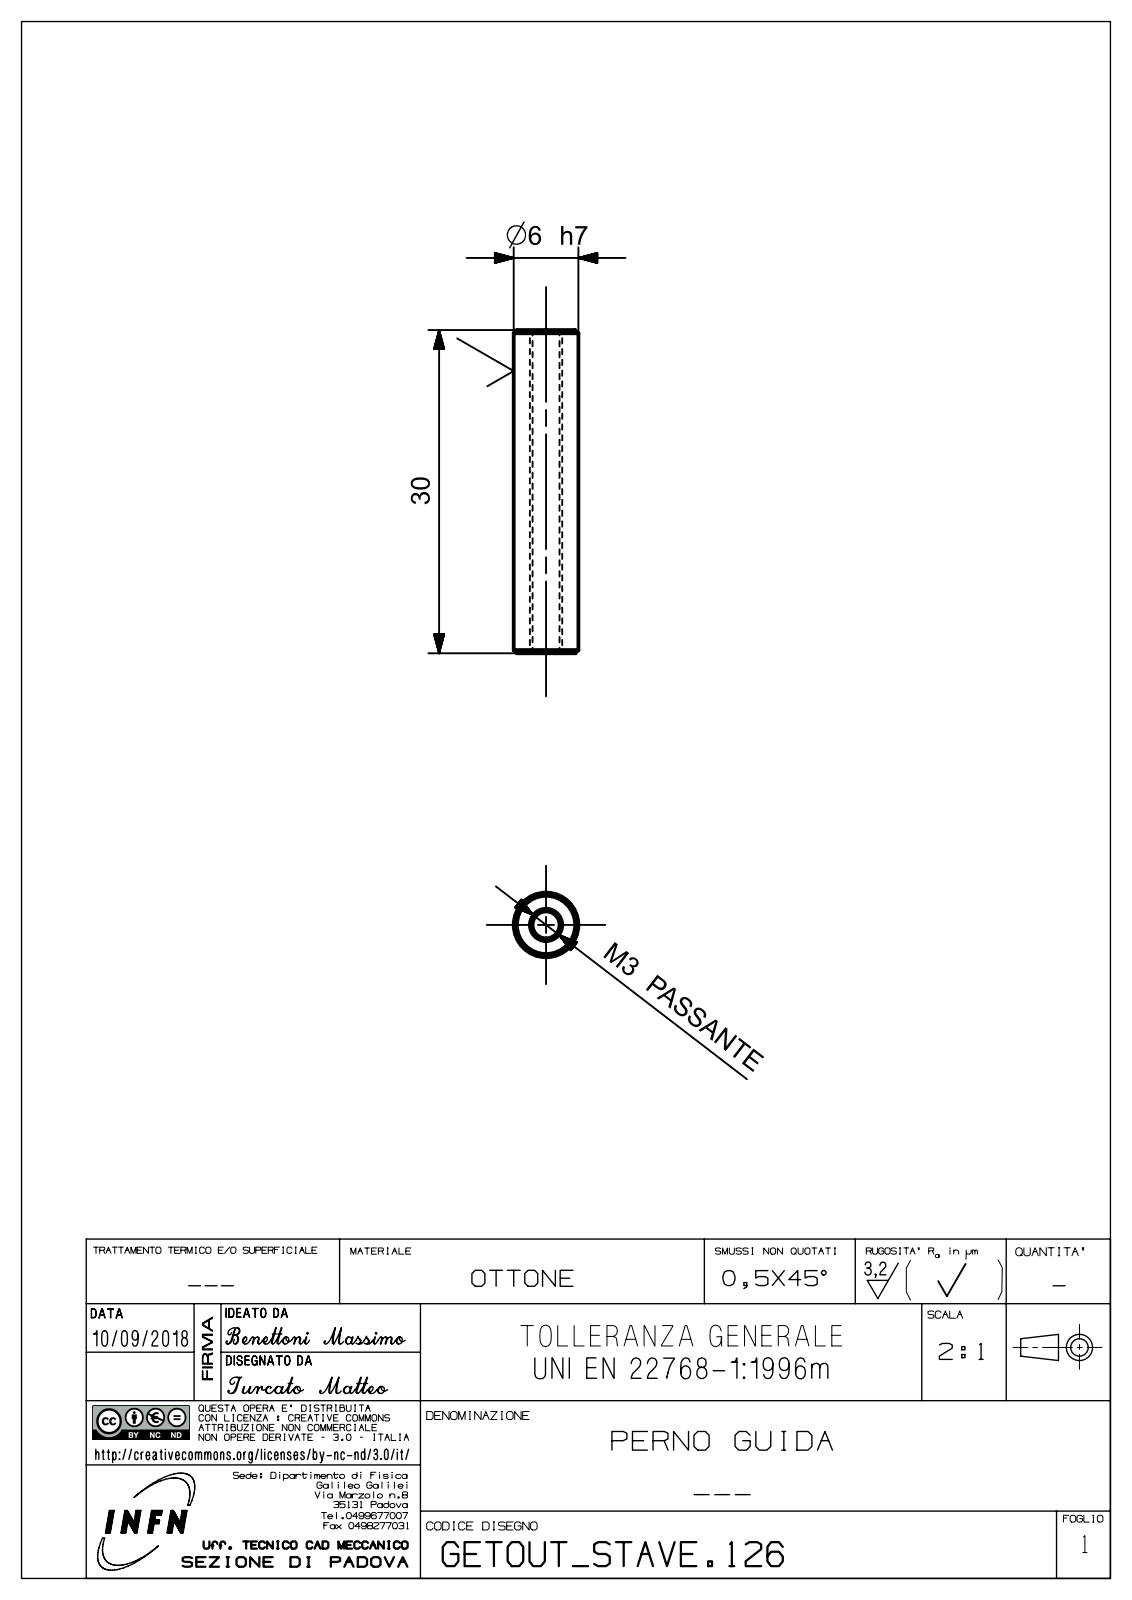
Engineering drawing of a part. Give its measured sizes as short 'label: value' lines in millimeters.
name: bezA730AE56cd3d
written by: SIEMENS PLM Software NX 12.0 (AUTOMOTIVE_DESIGN)
unit: mm
bodies: 1 solid, 8 faces (2 planar, 2 cylindrical, 4 other)
size: 30 × 6 × 6
volume: 699 mm³; area: 839 mm²
holes: 1× ⌀2.5
bosses: 1× ⌀6
face distances: 30
